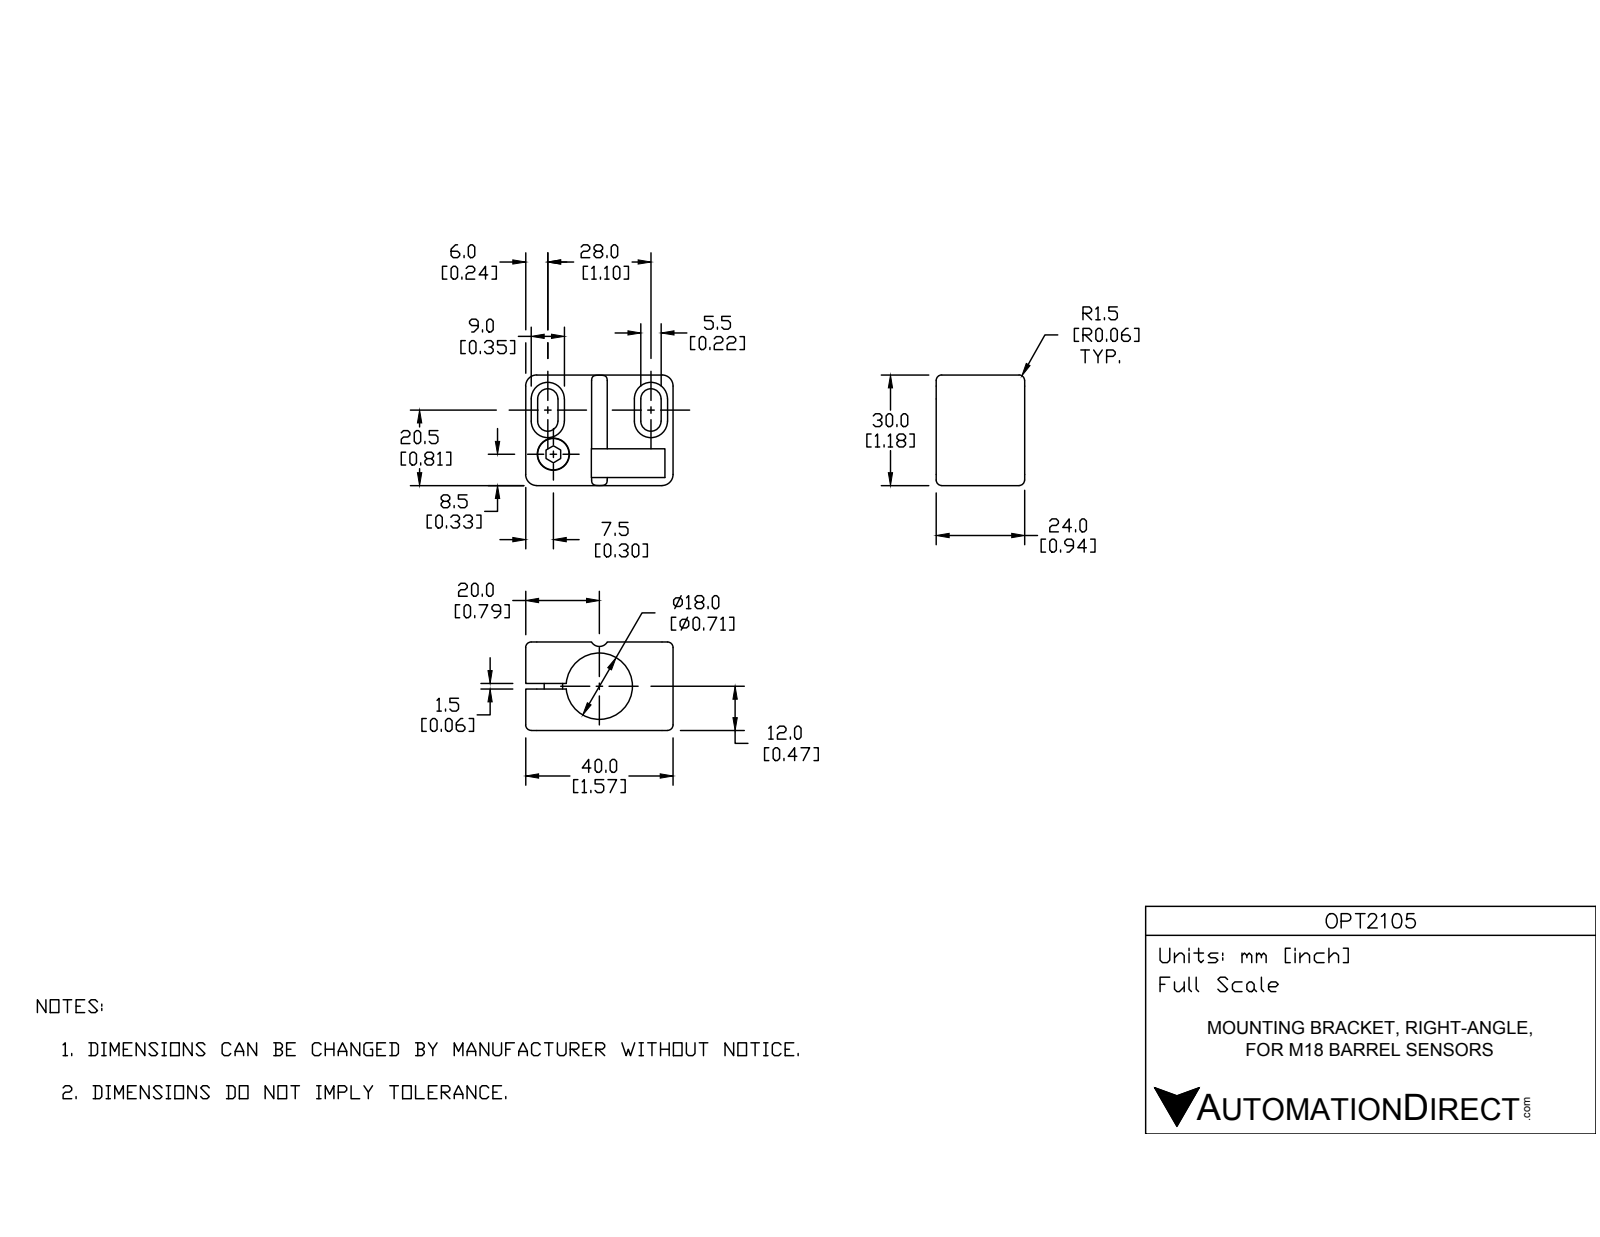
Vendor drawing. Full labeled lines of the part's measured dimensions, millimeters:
Part name (STEP PRODUCT): 56 10 30 18
STEP written by: Unknown (AUTOMOTIVE_DESIGN)
Units: millimetres
Bodies: 1 solid, 73 faces (34 planar, 29 cylindrical, 10 other)
Overall size (bounding box): 40 × 30 × 24
Volume: 15 787 mm³ · Surface area: 8 875 mm²
Round holes (diameter × count): ⌀5.5 ×1, ⌀8.7 ×1, ⌀18 ×1
Round bosses / shafts (diameter × count): ⌀8.5 ×1, ⌀5 ×1
Partial cylindrical surfaces — rounded edges, fillets, slot ends (radius × count): R1.5 ×8, R2.75 ×4, R3 ×4, R4.5 ×4, R2.5 ×1
Main face-to-face distances: 11.25, 1.5, 24, 40, 12.75, 30, 1.75, 7.25, 28, 22.5
